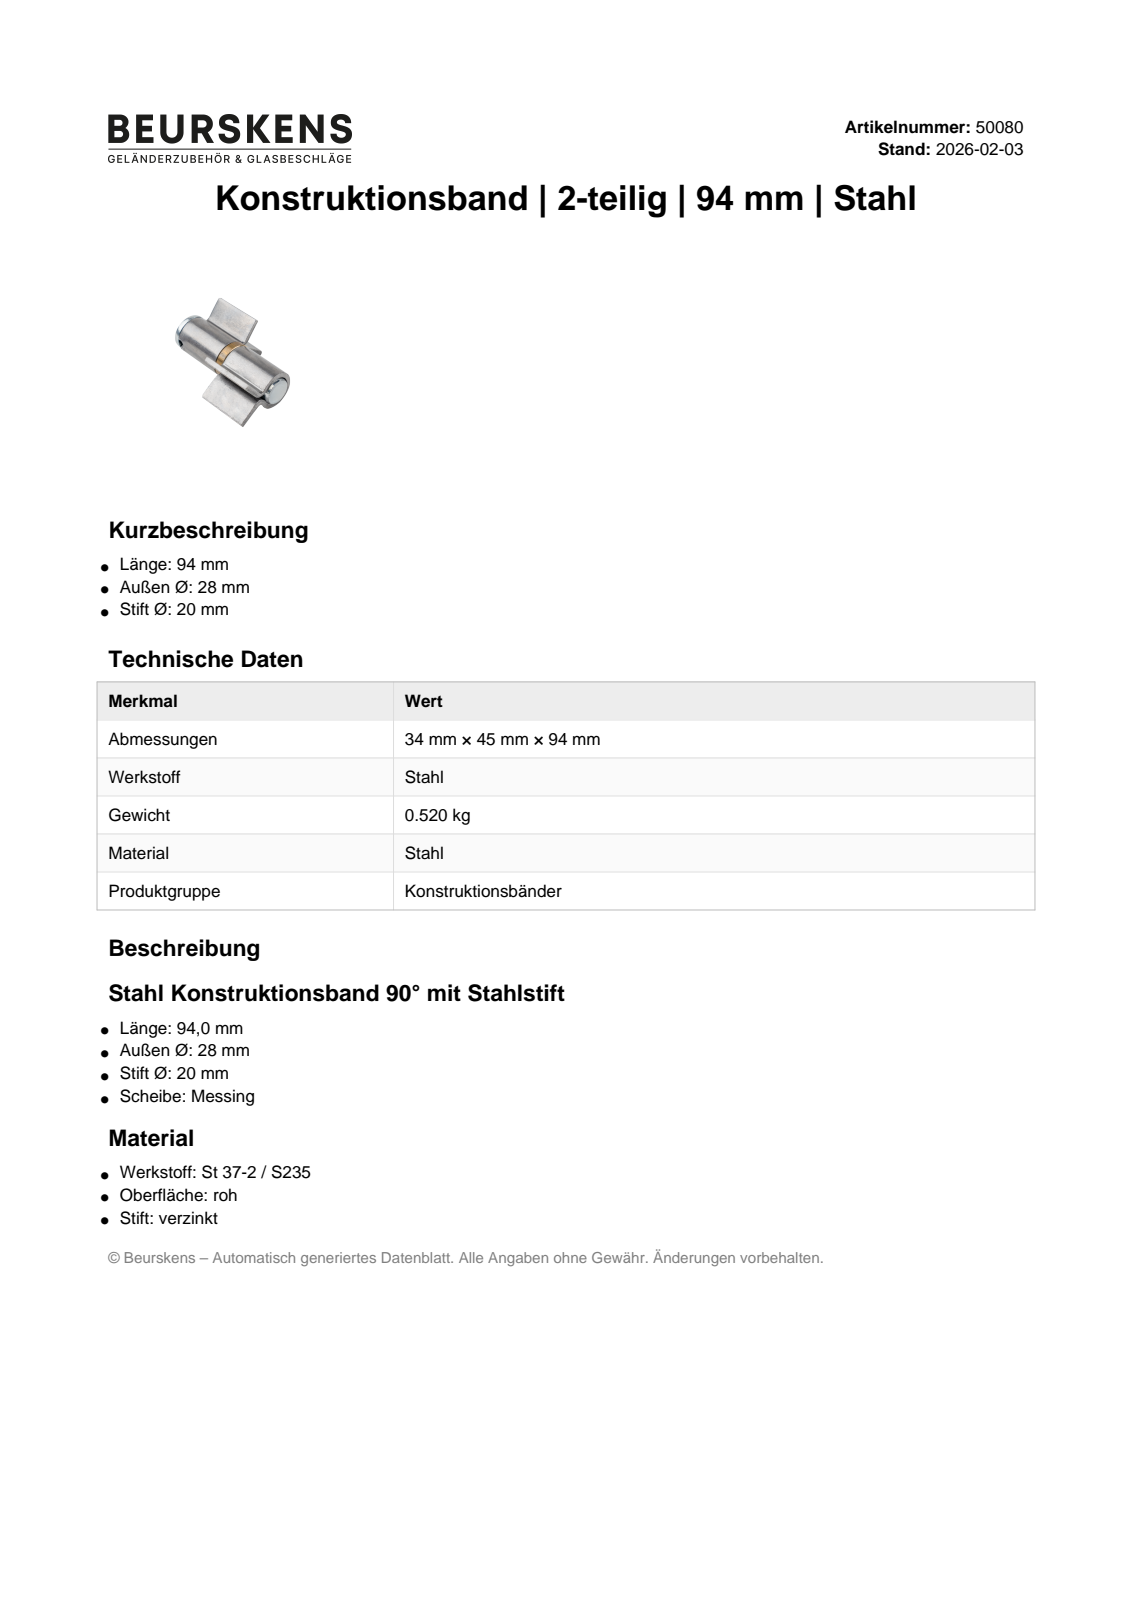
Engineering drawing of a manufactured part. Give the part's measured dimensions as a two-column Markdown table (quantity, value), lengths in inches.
| quantity | value |
| --- | --- |
| part name | 50080; 50080 Stift; 50080 Lasche; Messingscheibe 6 mm |
| STEP written by | Autodesk Inventor 2023 (AUTOMOTIVE_DESIGN) |
| units | inches |
| bodies | 4 solids, 47 faces (25 planar, 20 cylindrical, 2 other) |
| overall size | 3.701 × 1.847 × 1.847 |
| volume | 4.261 in³ |
| surface area | 45.19 in² |
| round holes (diameter × count) | 0.795 × 1 |
| round bosses / shafts (diameter × count) | 1.11 × 1, 1.102 × 1, 0.787 × 1 |
| partial cylindrical surfaces (radius × count) | 0.079 × 6 |
| main face-to-face distances | 0.157, 1.575, 1.811, 0.236, 2.028, 1.791, 0.217, 3.386, 3.602, 0.098 |
